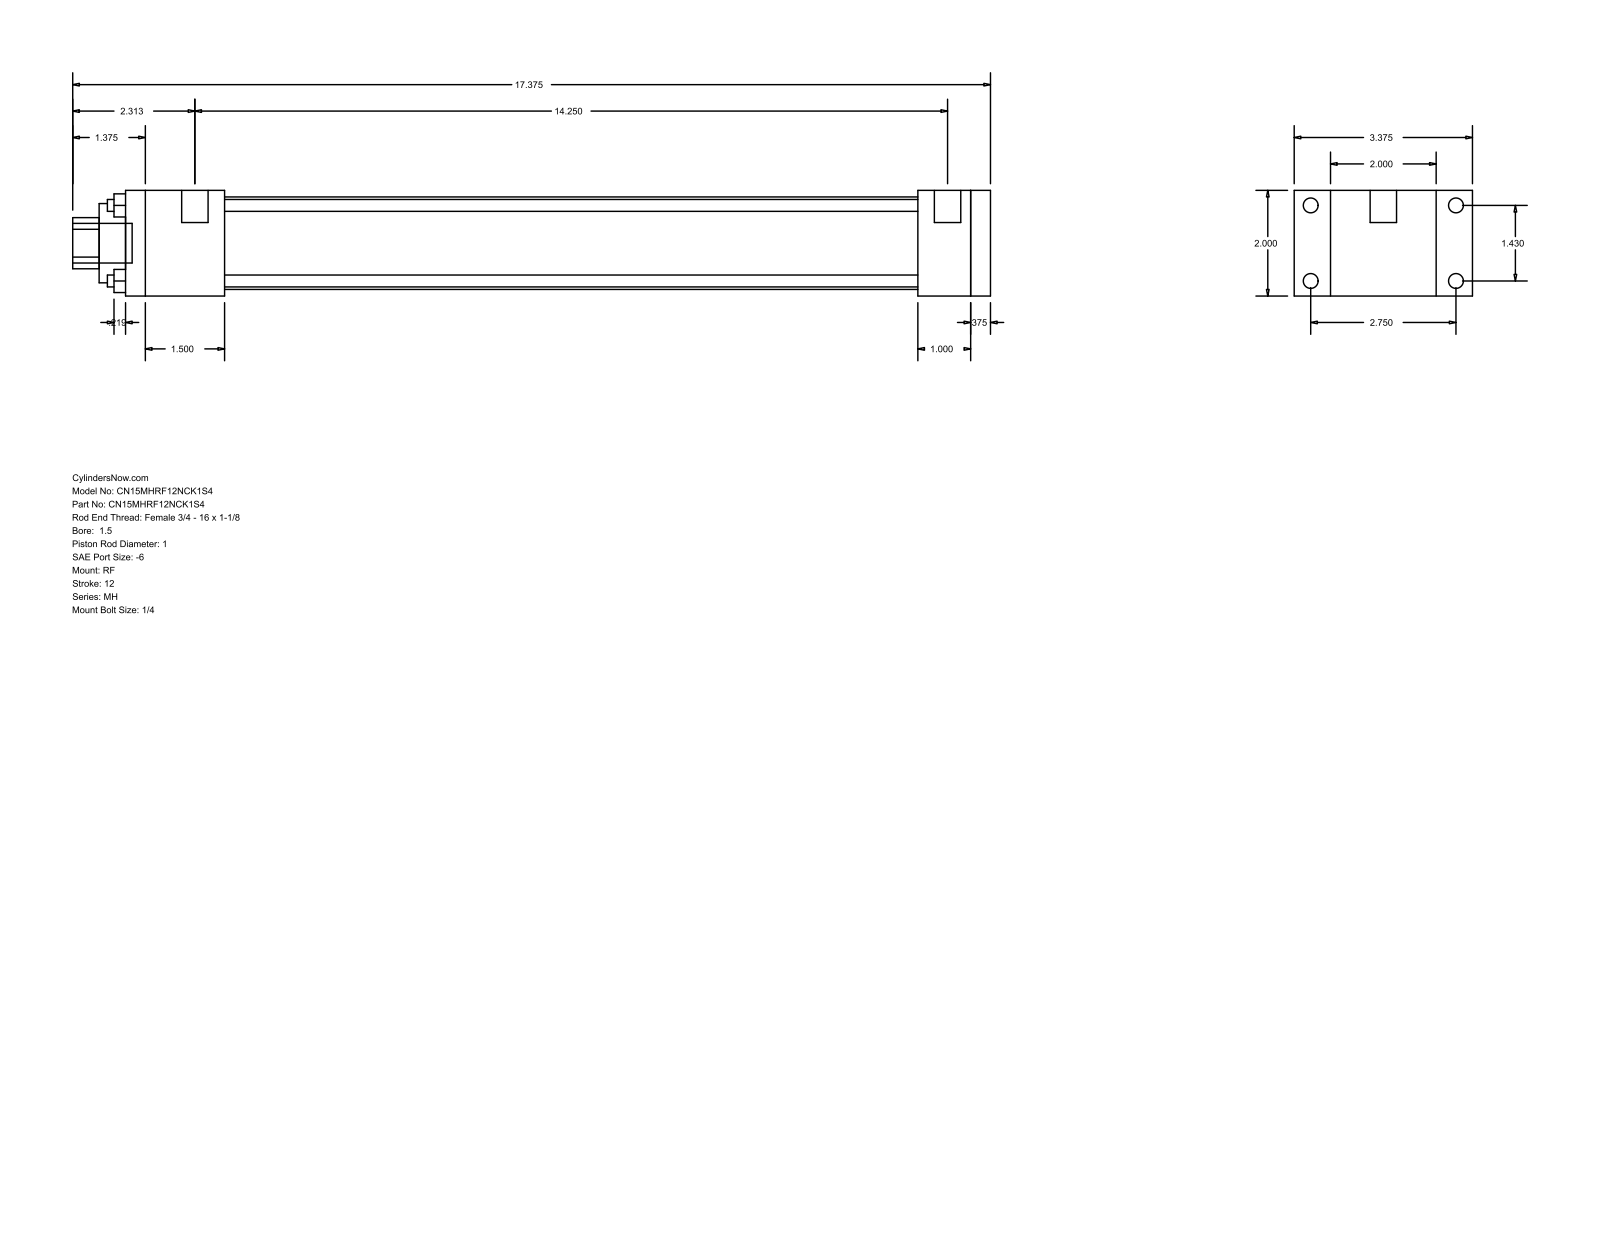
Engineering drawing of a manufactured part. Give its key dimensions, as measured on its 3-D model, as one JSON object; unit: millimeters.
{"part_name": "MH_RF__0150_1", "step_written_by": "GSSL Pune (CONFIG_CONTROL_DESIGN)", "units": "millimeters", "bodies": {"solids": 0, "faces": 92, "planar": 64, "cylindrical": 28, "other": 0}, "overall_size": [441.32, 85.72, 50.8], "round_holes": [[5.71, 4], [25.4, 1], [38.1, 1], [44.45, 1]], "round_bosses_or_shafts": [[7.14, 4], [5.56, 4], [12.7, 2], [19.05, 1]], "partial_cylinders_radius": [[12.29, 1]], "face_to_face_distances": [50.8, 9.52, 406.4, 25.4, 415.92, 17.46, 68.26, 381, 34.92, 47.63], "hole_center_spacings": [25.68, 36.32, 51.36]}
